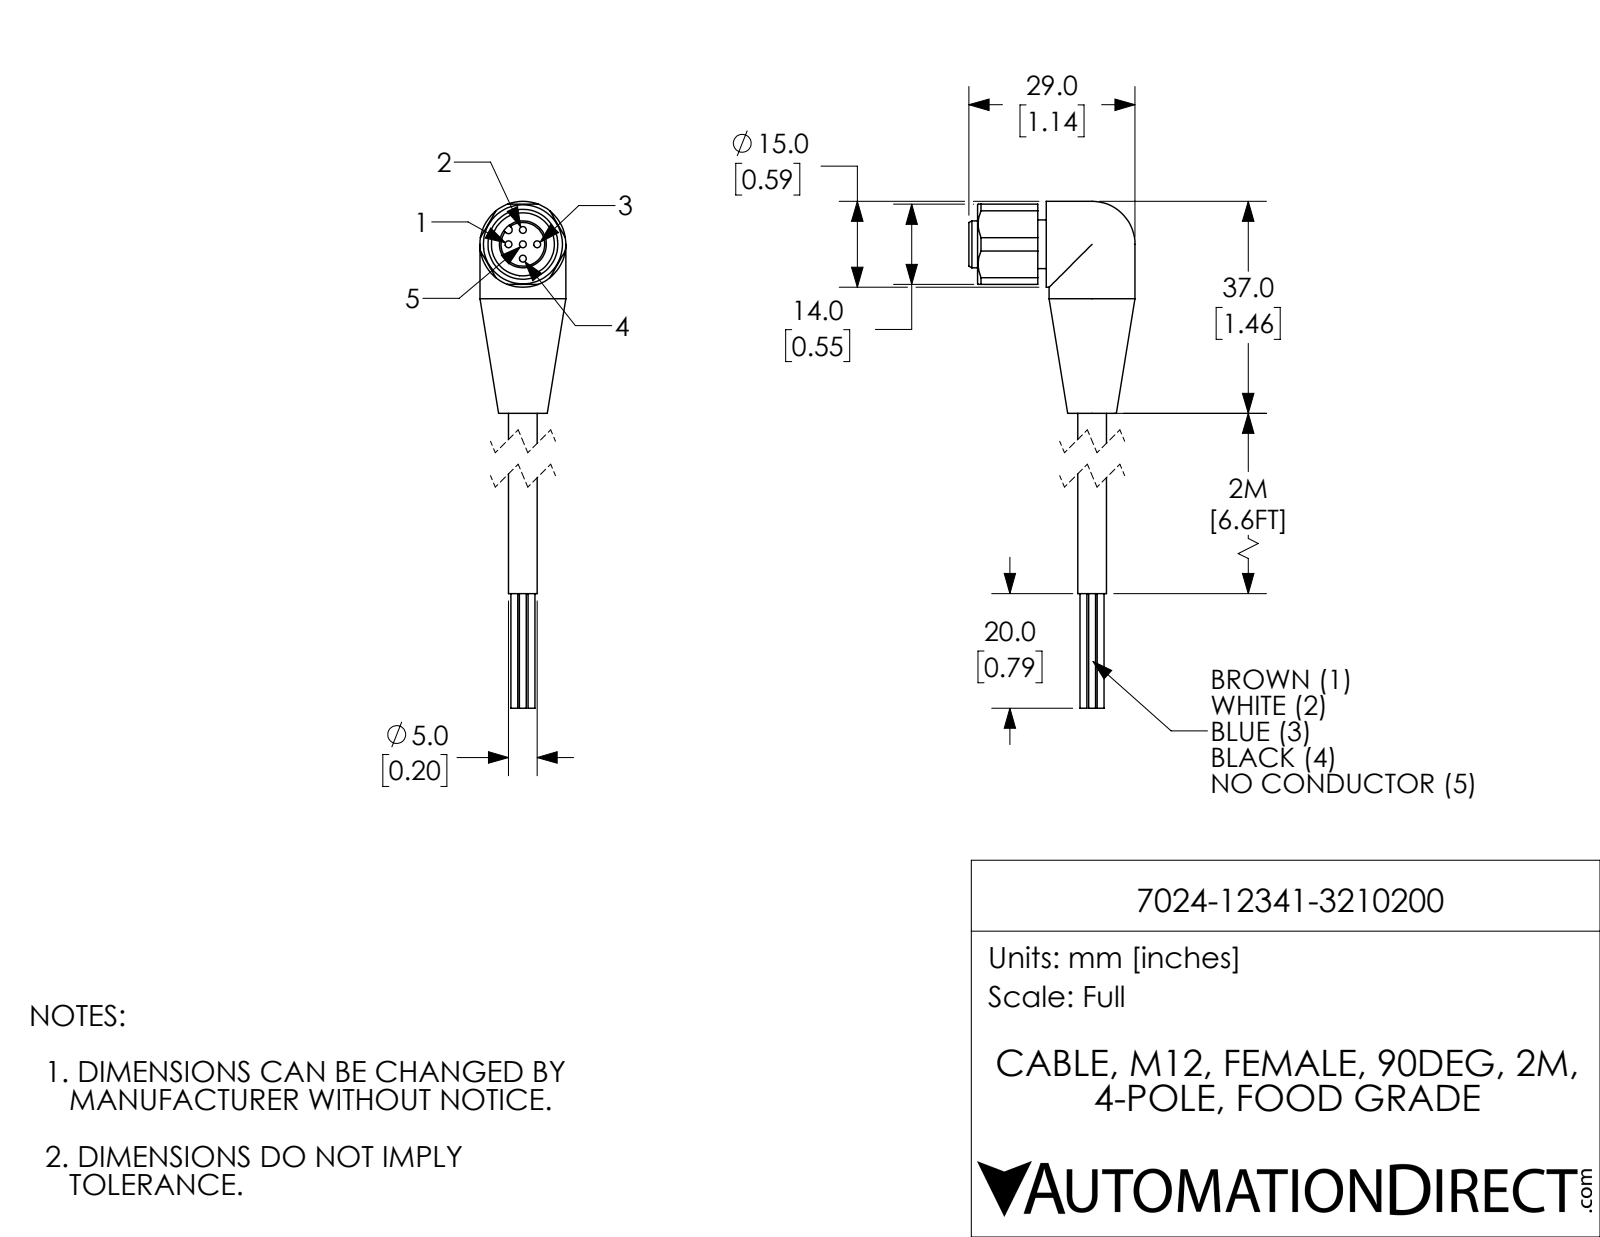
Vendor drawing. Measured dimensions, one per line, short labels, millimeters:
name: 7024-12341-3210200
written by: SolidWorks 2018 (AUTOMOTIVE_DESIGN)
unit: mm
bodies: 1 solid, 73 faces (25 planar, 38 cylindrical, 10 other)
size: 87 × 29 × 15
volume: 7 402 mm³; area: 3 886 mm²
holes: 5× ⌀1.2, 1× ⌀11
bosses: 4× ⌀1.2, 2× ⌀15, 1× ⌀8.5, 1× ⌀8.2, 1× ⌀5
rounds: 1× R0.65
face distances: 14, 1.5, 12, 4.5, 3, 13.5, 9, 22.5, 36.5, 10.5
hole spacings: 2.5, 3.54, 5
